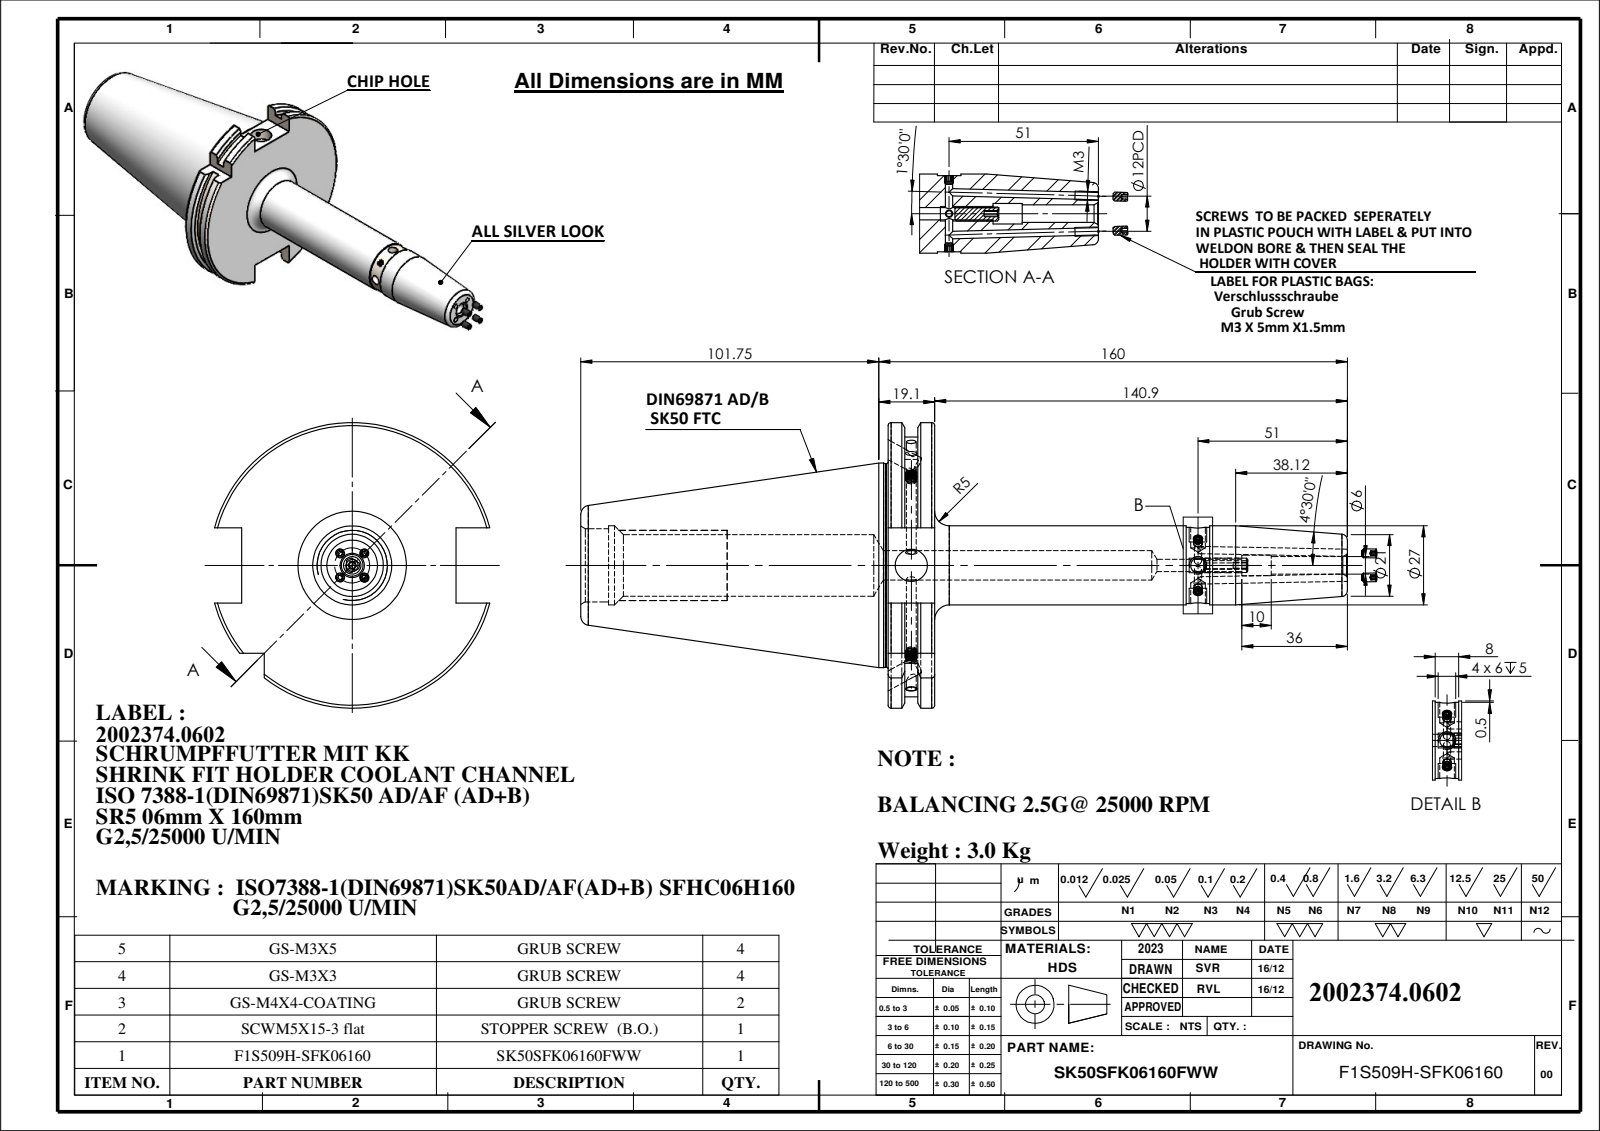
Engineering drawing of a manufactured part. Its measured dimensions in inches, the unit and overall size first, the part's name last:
Units: inches
Overall size (bounding box): 10.7 × 3.839 × 3.703
Round holes (diameter × count): ⌀0.098 ×8, ⌀0.197 ×2, ⌀0.236 ×2, ⌀0.13 ×1, ⌀0.165 ×1, ⌀0.236 ×1, ⌀0.275 ×1, ⌀0.394 ×1, ⌀0.433 ×1, ⌀0.827 ×1, ⌀0.984 ×1
Round bosses / shafts (diameter × count): ⌀0.118 ×8, ⌀0.157 ×2, ⌀2.75 ×1, ⌀2.734 ×1, ⌀1.063 ×1, ⌀1.024 ×1
Partial cylindrical surfaces — rounded edges, fillets, slot ends (radius × count): R0.098 ×1, R1.768 ×1, R1.919 ×1
Main face-to-face distances: 0.626, 0.223, 0.403, 0.399, 0.176, 0.227, 4.132, 4.355, 4.531, 4.758
Hole centre spacings: 3.854
Volume: 23.82 in³ · Surface area: 97.36 in²
Bodies: 12 solids, 445 faces (155 planar, 126 cylindrical, 164 other)
Part name (STEP PRODUCT): SCWM5X15-3 flat; SK50SFK06160FWW; F1S509H-SFK06160; socket set screw flat point_din_DIN 913 - M3 x 5-N (+2 more)
STEP written by: SolidWorks 2023 (CONFIG_CONTROL_DESIGN)
